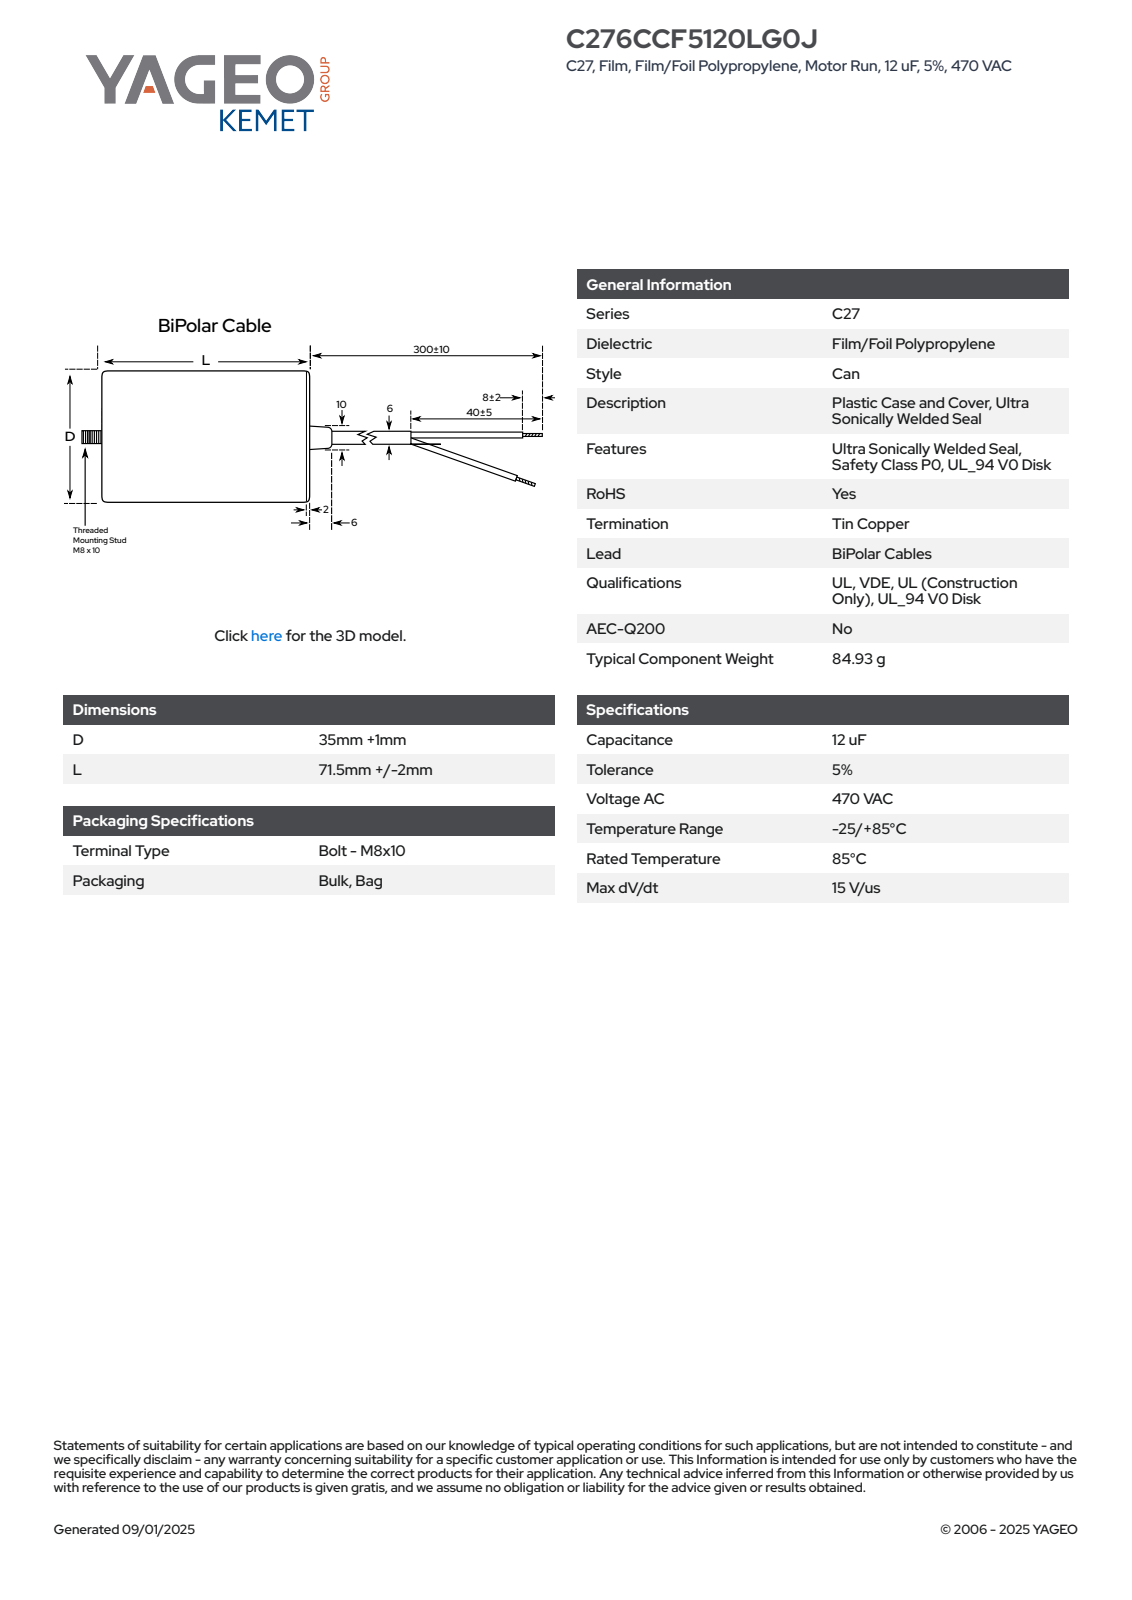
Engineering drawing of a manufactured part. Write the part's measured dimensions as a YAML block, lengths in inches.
part_name: "CFM_KC27BI_35X71.5_D36L73.5"
step_written_by: "SolidWorks 2014 (AUTOMOTIVE_DESIGN)"
units: inches
bodies: {solids: 2, faces: 82, planar: 28, cylindrical: 15, other: 39}
overall_size: [3.524, 1.418, 1.417]
volume: 4.518
surface_area: 17.05
round_holes:
  - {diameter: 1.26, count: 1}
round_bosses_or_shafts:
  - {diameter: 1.417, count: 1}
  - {diameter: 0.315, count: 1}
partial_cylinders:
  - {radius: 0.709, count: 1}
face_to_face_distances: [2.815, 2.894, 0.079, 0.394, 3.209, 3.287, 3.524, 3.13, 0.315, 0.236]
